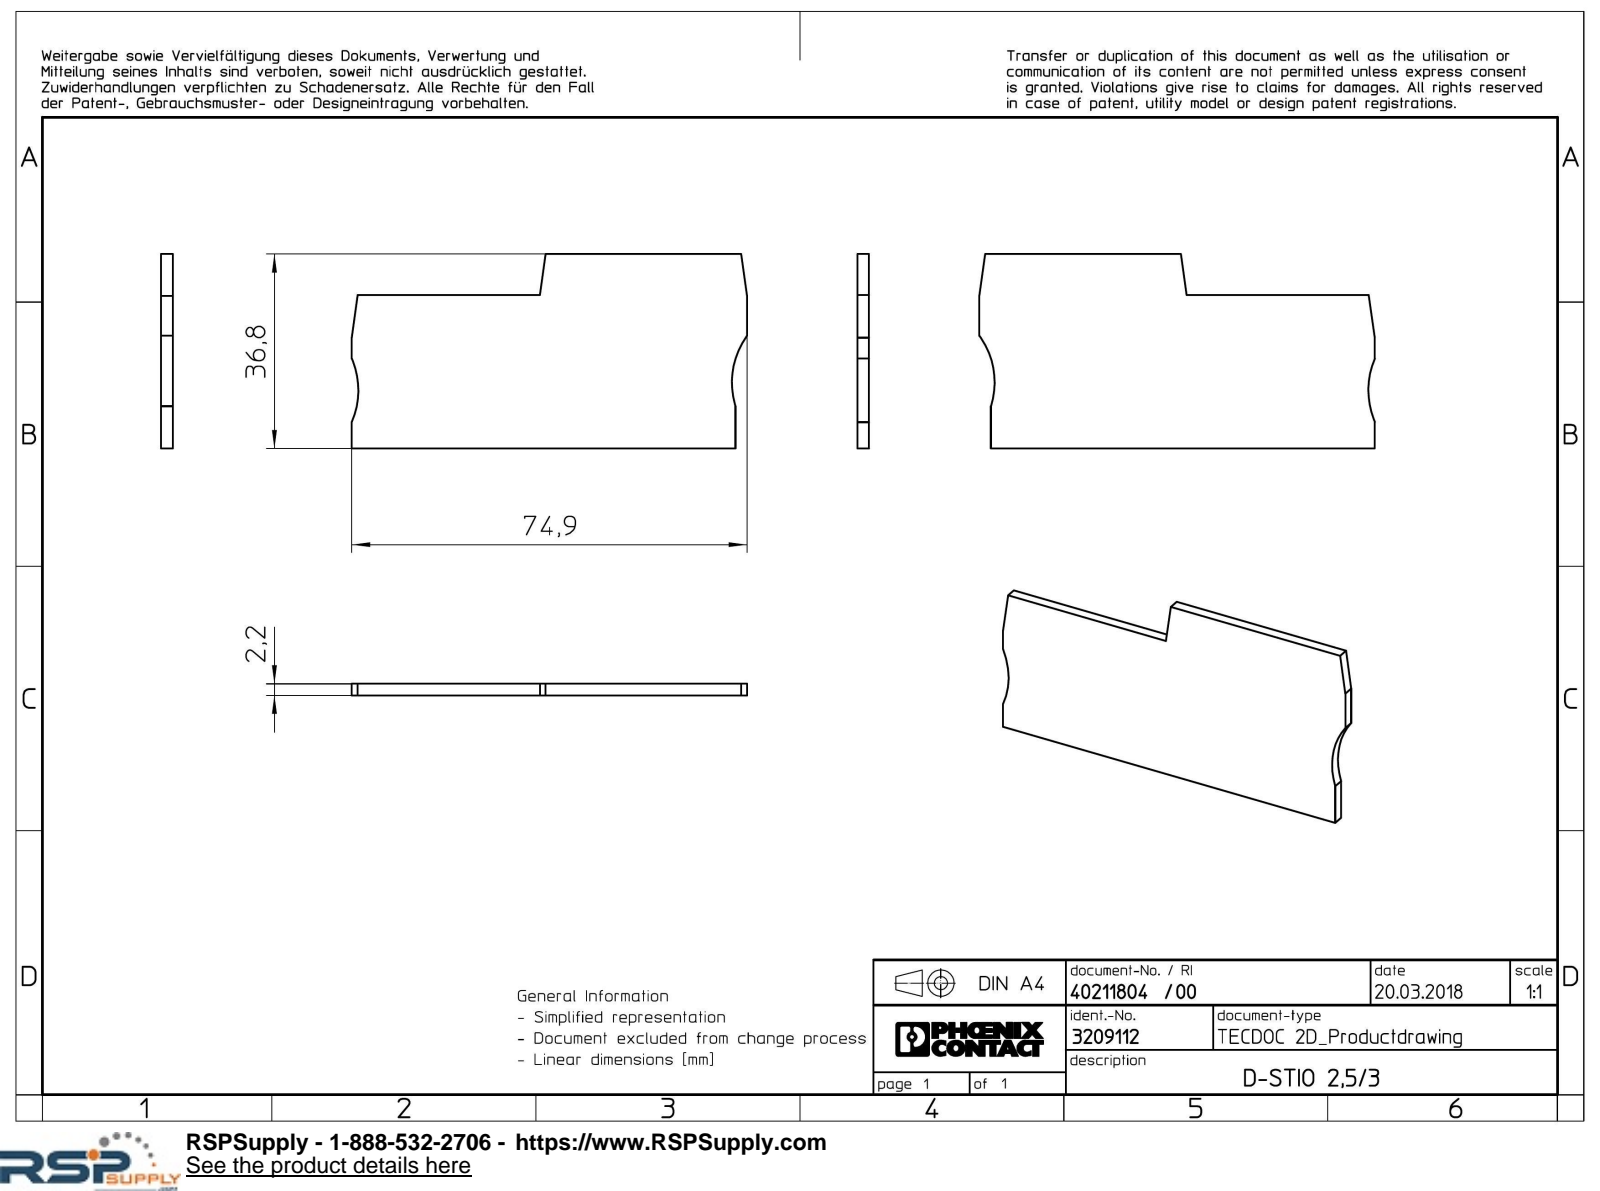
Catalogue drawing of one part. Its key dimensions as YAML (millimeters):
part_name: "D_STIO_25_3"
step_written_by: "Creo Elements/Direct Modeling 18.1I 14-Aug-2016 (C) Parametric Technology GmbH (AUTOMOTIVE_DESIGN)"
units: millimeters
bodies: {solids: 1, faces: 14, planar: 12, cylindrical: 2, other: 0}
overall_size: [74.89, 36.8, 2.2]
volume: 5301
surface_area: 5301
partial_cylinders:
  - {radius: 15, count: 2}
face_to_face_distances: [2.2, 36.8, 29.05, 7.75, 72.7, 34.16, 74.89, 2.19]
